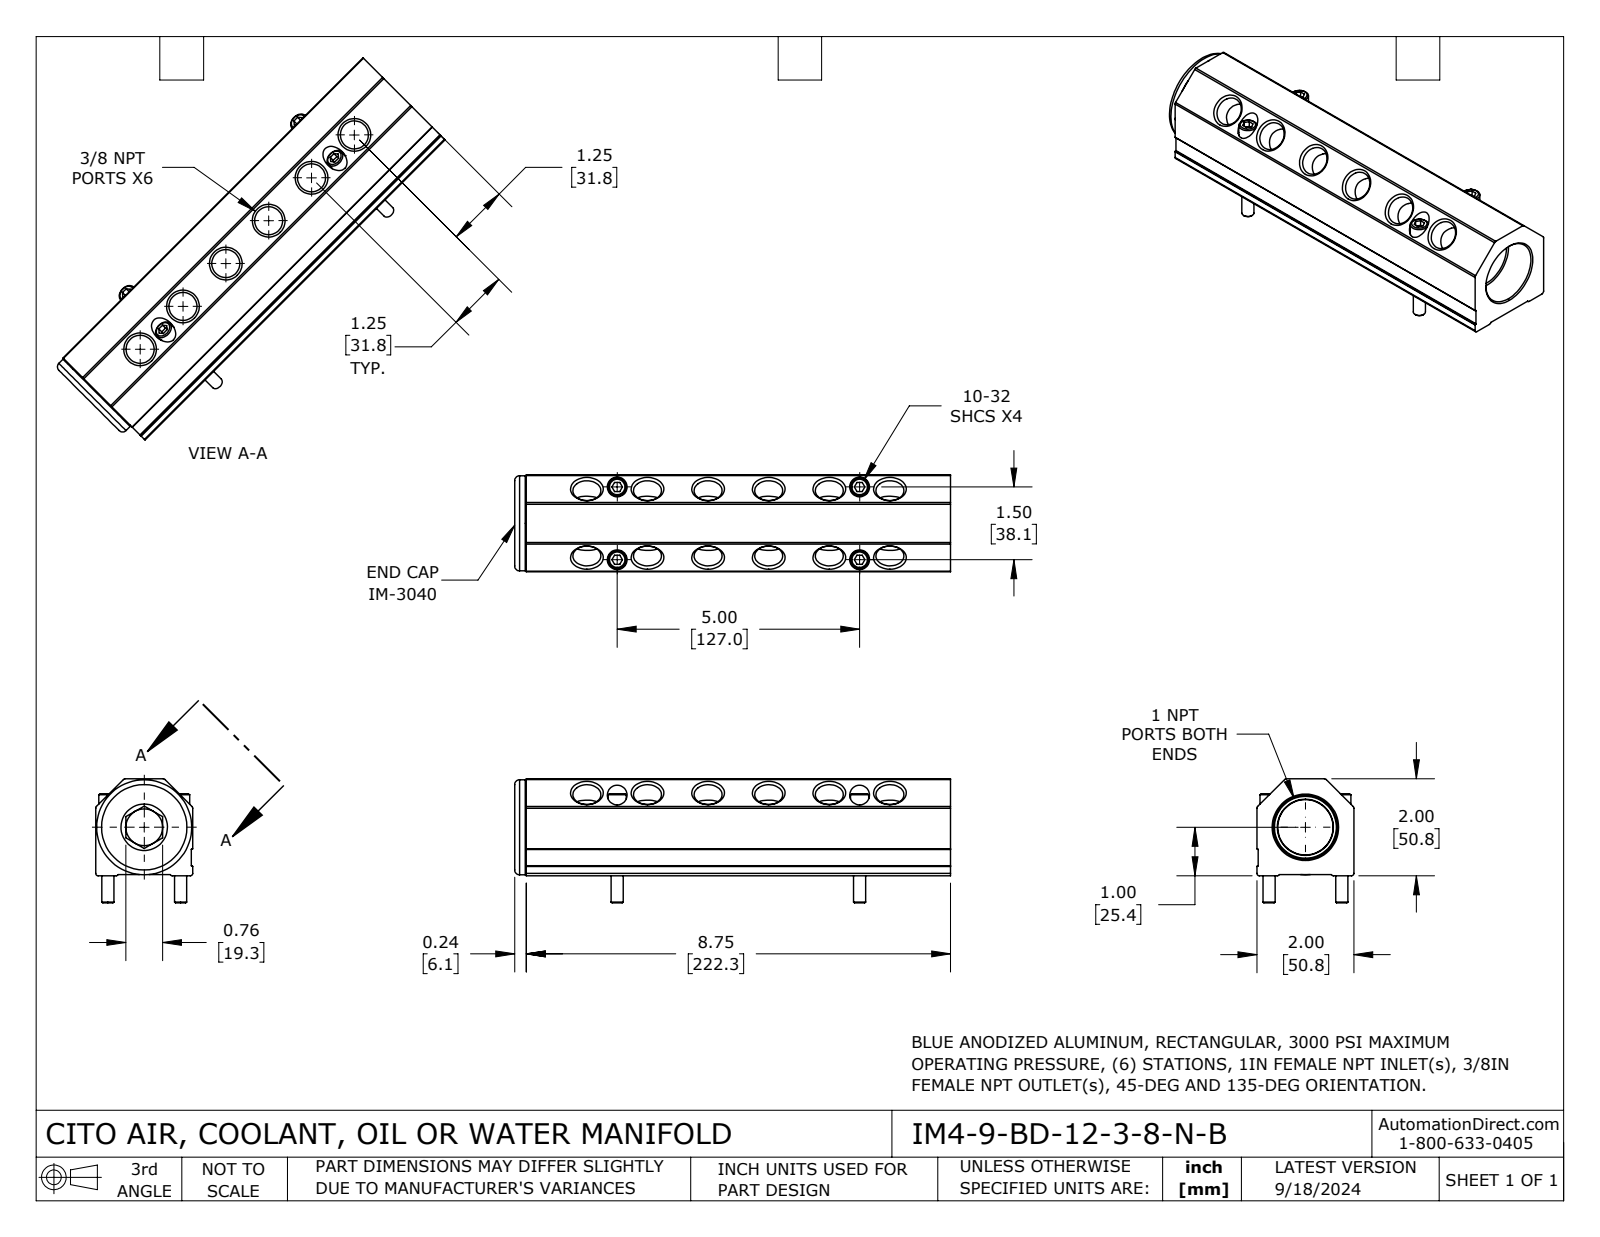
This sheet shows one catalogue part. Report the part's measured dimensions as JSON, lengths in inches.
{"part_name": "IM4-9-BD-12-3-8-N-B", "step_written_by": "SolidWorks 2023 (CONFIG_CONTROL_DESIGN)", "units": "inches", "bodies": {"solids": 6, "faces": 229, "planar": 81, "cylindrical": 82, "other": 66}, "overall_size": [8.99, 2.56, 2], "volume_in3": 21.74, "surface_area_in2": 130, "round_holes": [[0.578, 12], [0.266, 4], [0.406, 4], [0.758, 1], [1.156, 1], [1.637, 1]], "round_bosses_or_shafts": [[0.375, 4], [0.25, 4], [1.96, 1], [1.359, 1], [1.293, 1], [1.14, 1]], "partial_cylinders_radius": [[0.05, 8], [0.01, 4]], "face_to_face_distances": [2, 1.975, 0.025, 0.028, 1.972, 8.75, 0.24, 8.99, 0.764, 0.524], "hole_center_spacings": [1.25, 2.5, 3.75, 5, 1.5, 5.22, 6.25]}
